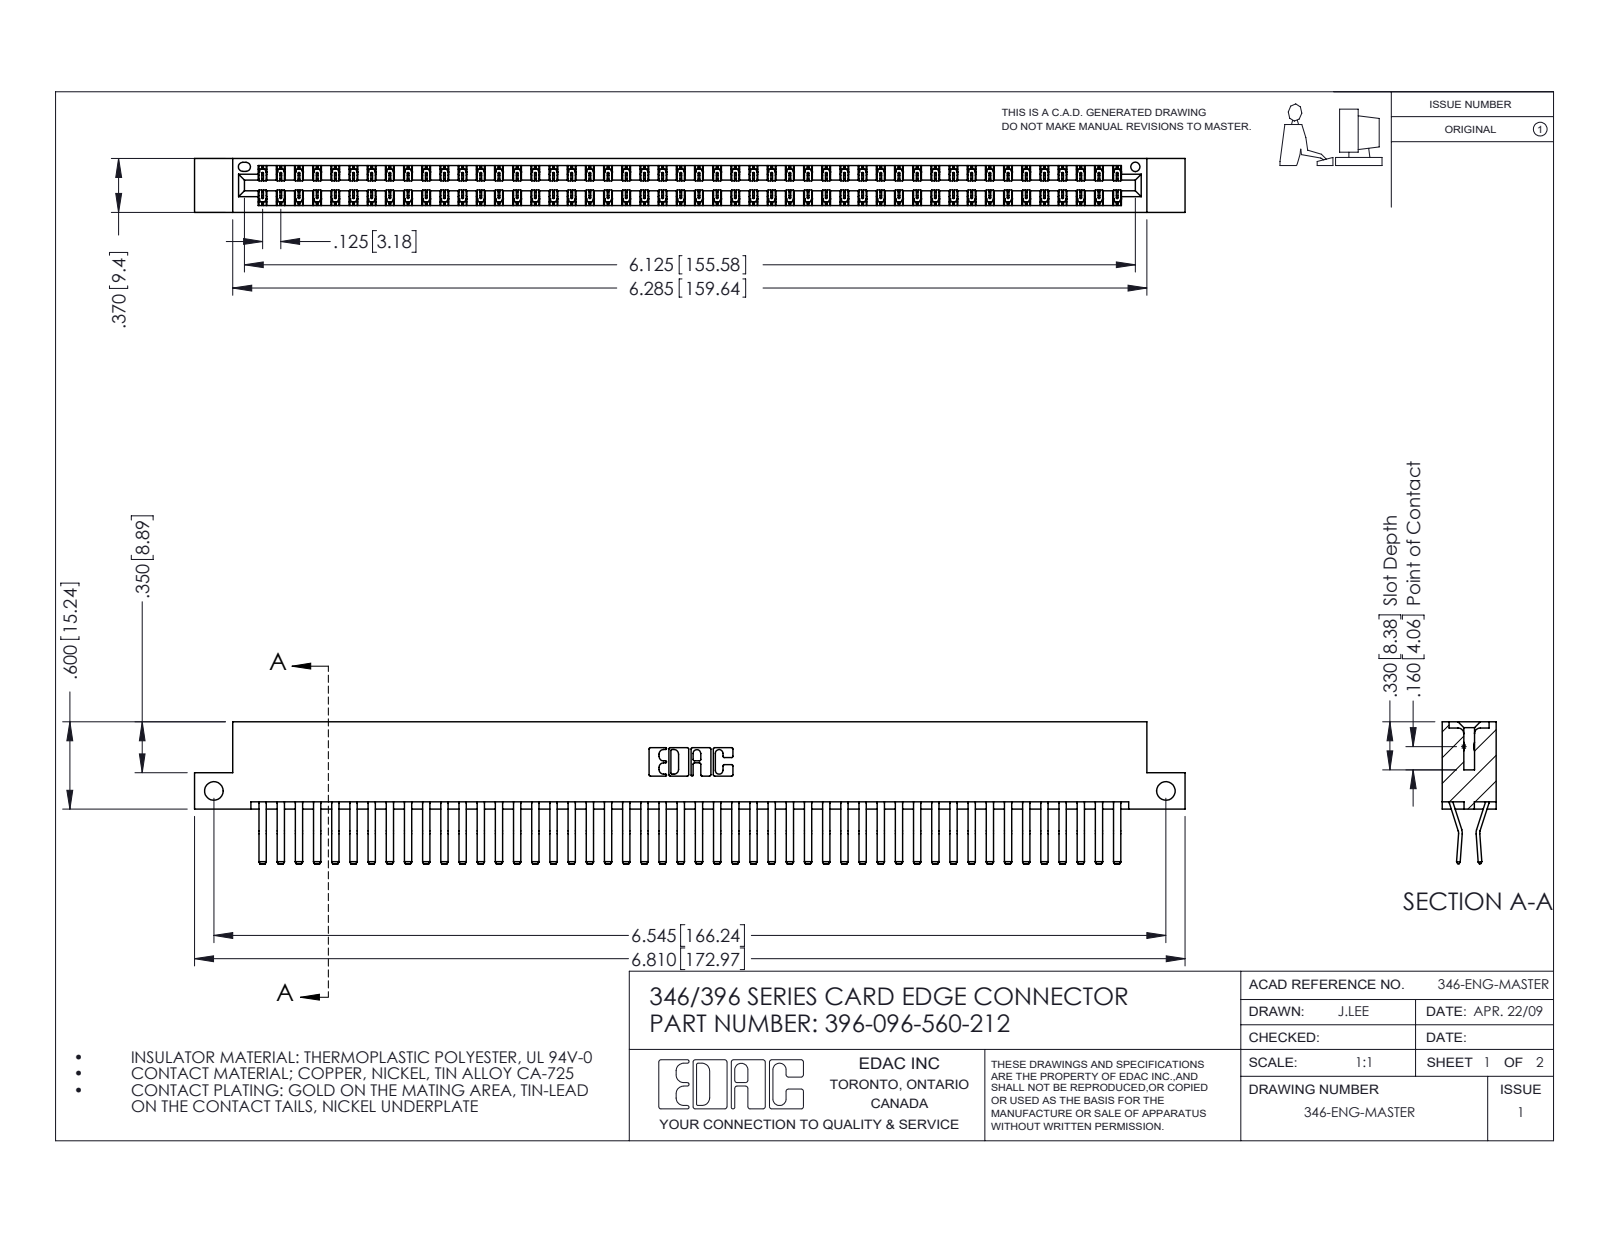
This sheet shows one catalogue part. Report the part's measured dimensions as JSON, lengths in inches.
{"part_name": "345-292-001_560 Tail; 396-096-560-212; 346 Part_Flush Mounting Lugs - Side Mount", "step_written_by": "SolidWorks 2016 (CONFIG_CONTROL_DESIGN)", "units": "inches", "bodies": {"solids": 97, "faces": 5306, "planar": 3436, "cylindrical": 1870, "other": 0}, "overall_size": [6.81, 0.975, 0.37], "volume_in3": 1.065, "surface_area_in2": 39.73, "round_holes": [[0.128, 2], [0.064, 1]], "partial_cylinders_radius": [[0.006, 144], [0.01, 22], [0.007, 6], [0.031, 6], [0.026, 3], [0.01, 2], [0.014, 2], [0.022, 2]], "face_to_face_distances": [0.048, 0.322, 0.37, 0.025, 0.25, 0.072, 0.298, 0.275, 0.148, 0.222], "hole_center_spacings": [6.545]}
